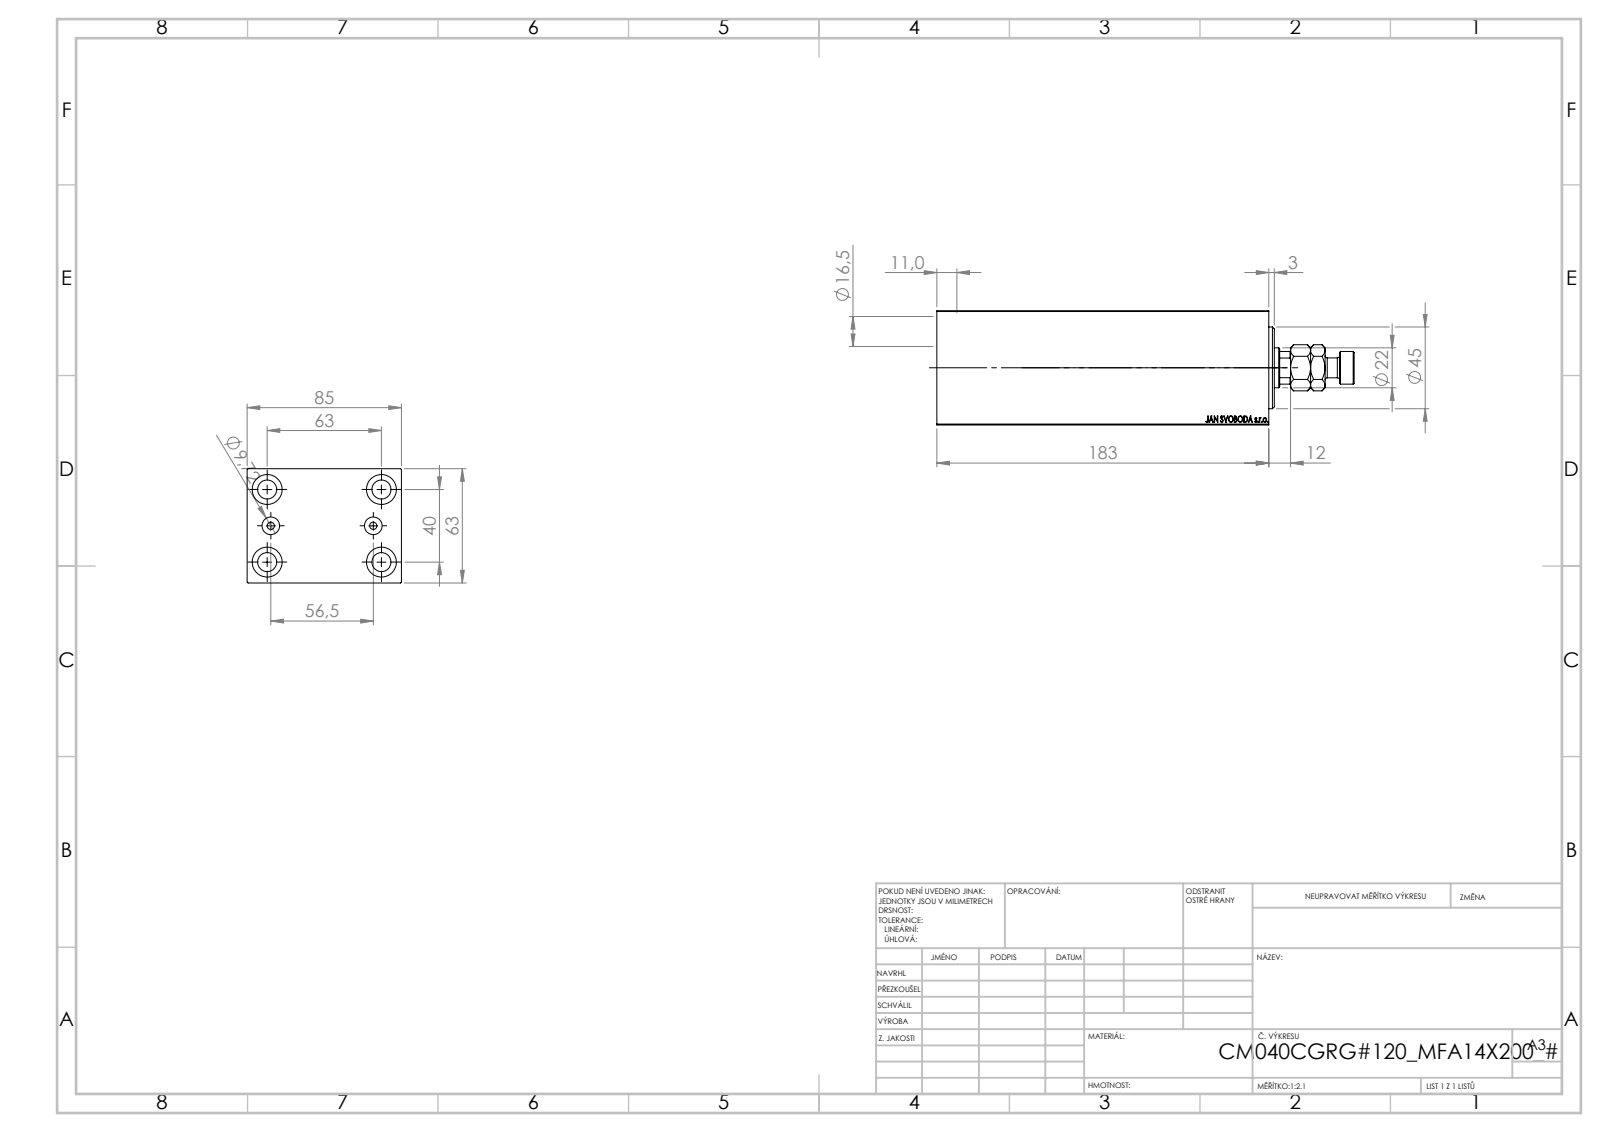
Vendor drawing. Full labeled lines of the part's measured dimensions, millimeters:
Part name (STEP PRODUCT): V450CM_VC_B; MFA; V450CM_C_VCP; V450CM_C_Body
STEP written by: SolidWorks 2019 (CONFIG_CONTROL_DESIGN)
Units: millimetres
Bodies: 4 solids, 910 faces (424 planar, 60 cylindrical, 426 other)
Overall size (bounding box): 230 × 85 × 63
Volume: 809 965 mm³ · Surface area: 145 537 mm²
Round holes (diameter × count): ⌀10.5 ×4, ⌀16.5 ×4, ⌀4 ×2, ⌀9.72 ×2, ⌀12.5 ×1, ⌀22 ×1, ⌀25.5 ×1, ⌀40 ×1, ⌀42 ×1, ⌀45 ×1
Round bosses / shafts (diameter × count): ⌀18 ×1, ⌀11 ×1
Partial cylindrical surfaces — rounded edges, fillets, slot ends (radius × count): R10.5 ×1
Main face-to-face distances: 63, 85, 183, 12, 171, 28.6, 142.4, 154.4, 11, 172
Hole centre spacings: 20.26, 37.31, 63.01, 28.25, 40, 63, 74.63, 56.5
